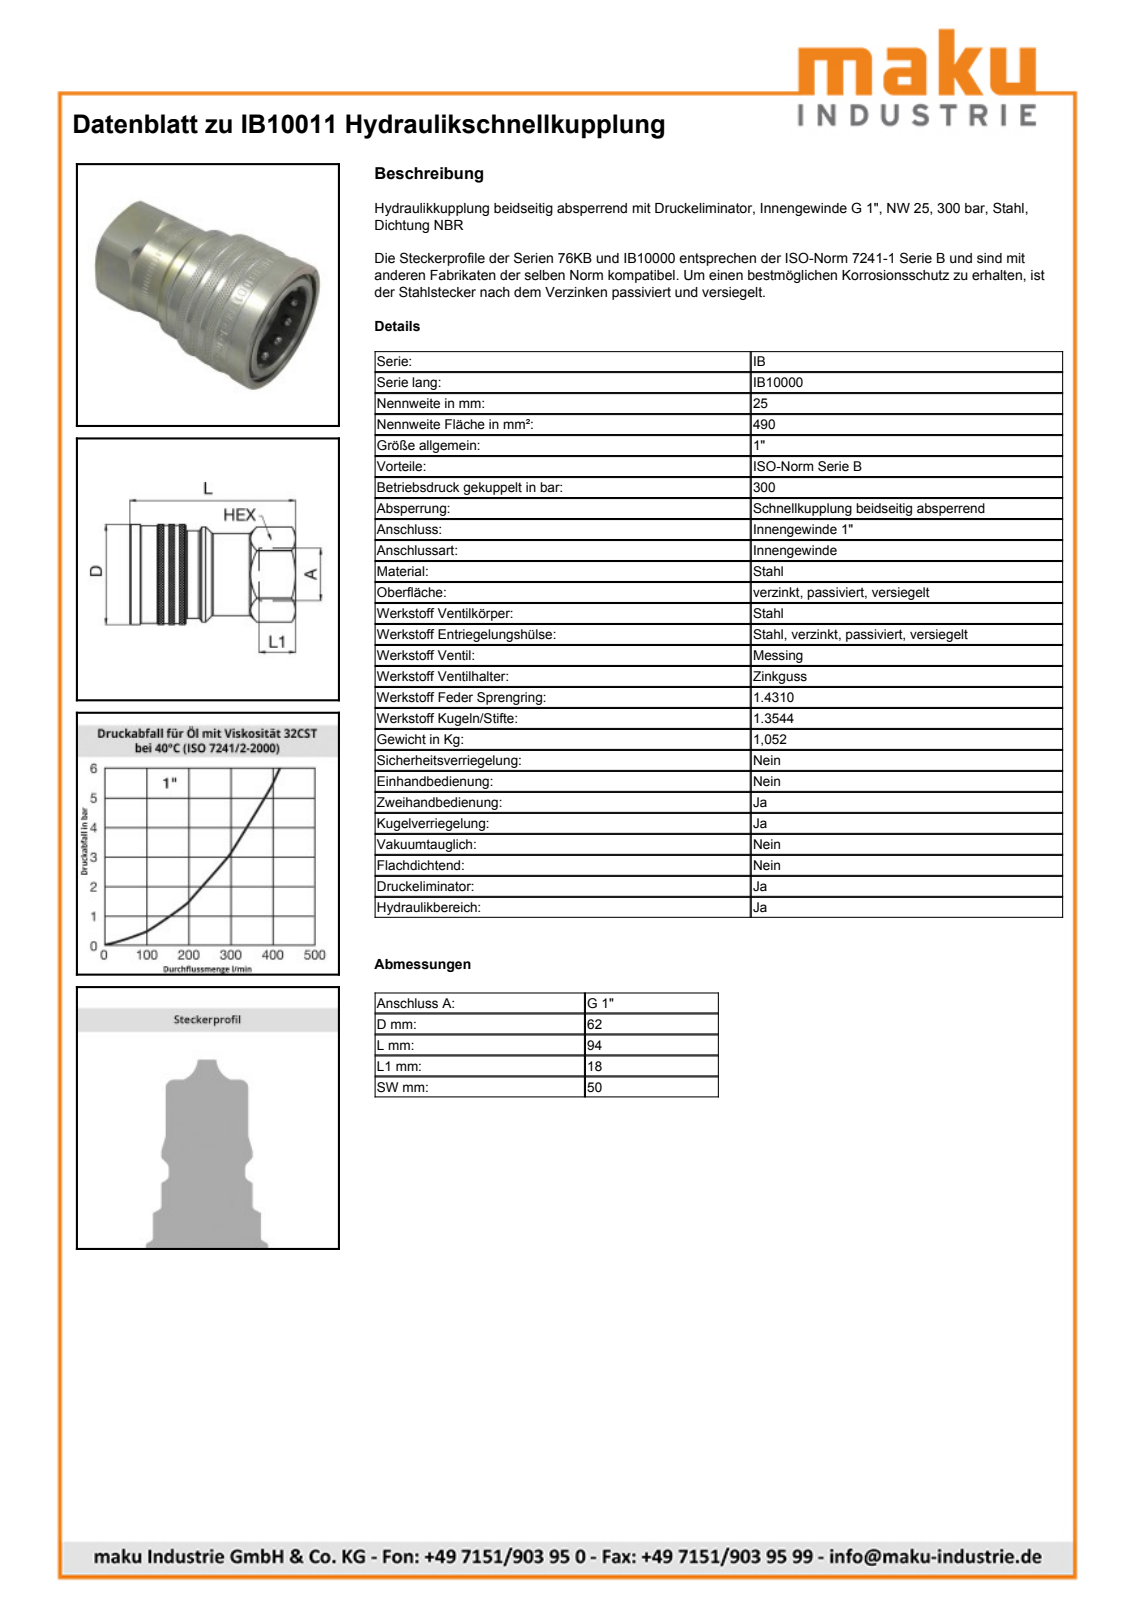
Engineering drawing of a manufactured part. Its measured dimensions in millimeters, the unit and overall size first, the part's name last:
Units: millimetres
Overall size (bounding box): 94.25 × 62 × 62
Round holes (diameter × count): ⌀1 ×2, ⌀2.85 ×1, ⌀3.93 ×1, ⌀24.4 ×1, ⌀30.6 ×1, ⌀37.9 ×1, ⌀38 ×1, ⌀40.6 ×1, ⌀44.2 ×1, ⌀49.5 ×1, ⌀54 ×1, ⌀55.2 ×1
Round bosses / shafts (diameter × count): ⌀62 ×1, ⌀61 ×1, ⌀60.8 ×1, ⌀56 ×1, ⌀55 ×1, ⌀54.4 ×1, ⌀49.3 ×1, ⌀44 ×1
Partial cylindrical surfaces — rounded edges, fillets, slot ends (radius × count): R21.69 ×1, R23.65 ×1
Main face-to-face distances: 50, 19.36, 94.25, 74.89, 54.1, 34.74, 40.15, 56.75, 37.39, 2.65
Volume: 167 170 mm³ · Surface area: 37 942 mm²
Bodies: 1 solid, 318 faces (28 planar, 86 cylindrical, 204 other)
Part name (STEP PRODUCT): IB10011
STEP written by: SolidWorks 2009 (AUTOMOTIVE_DESIGN)
